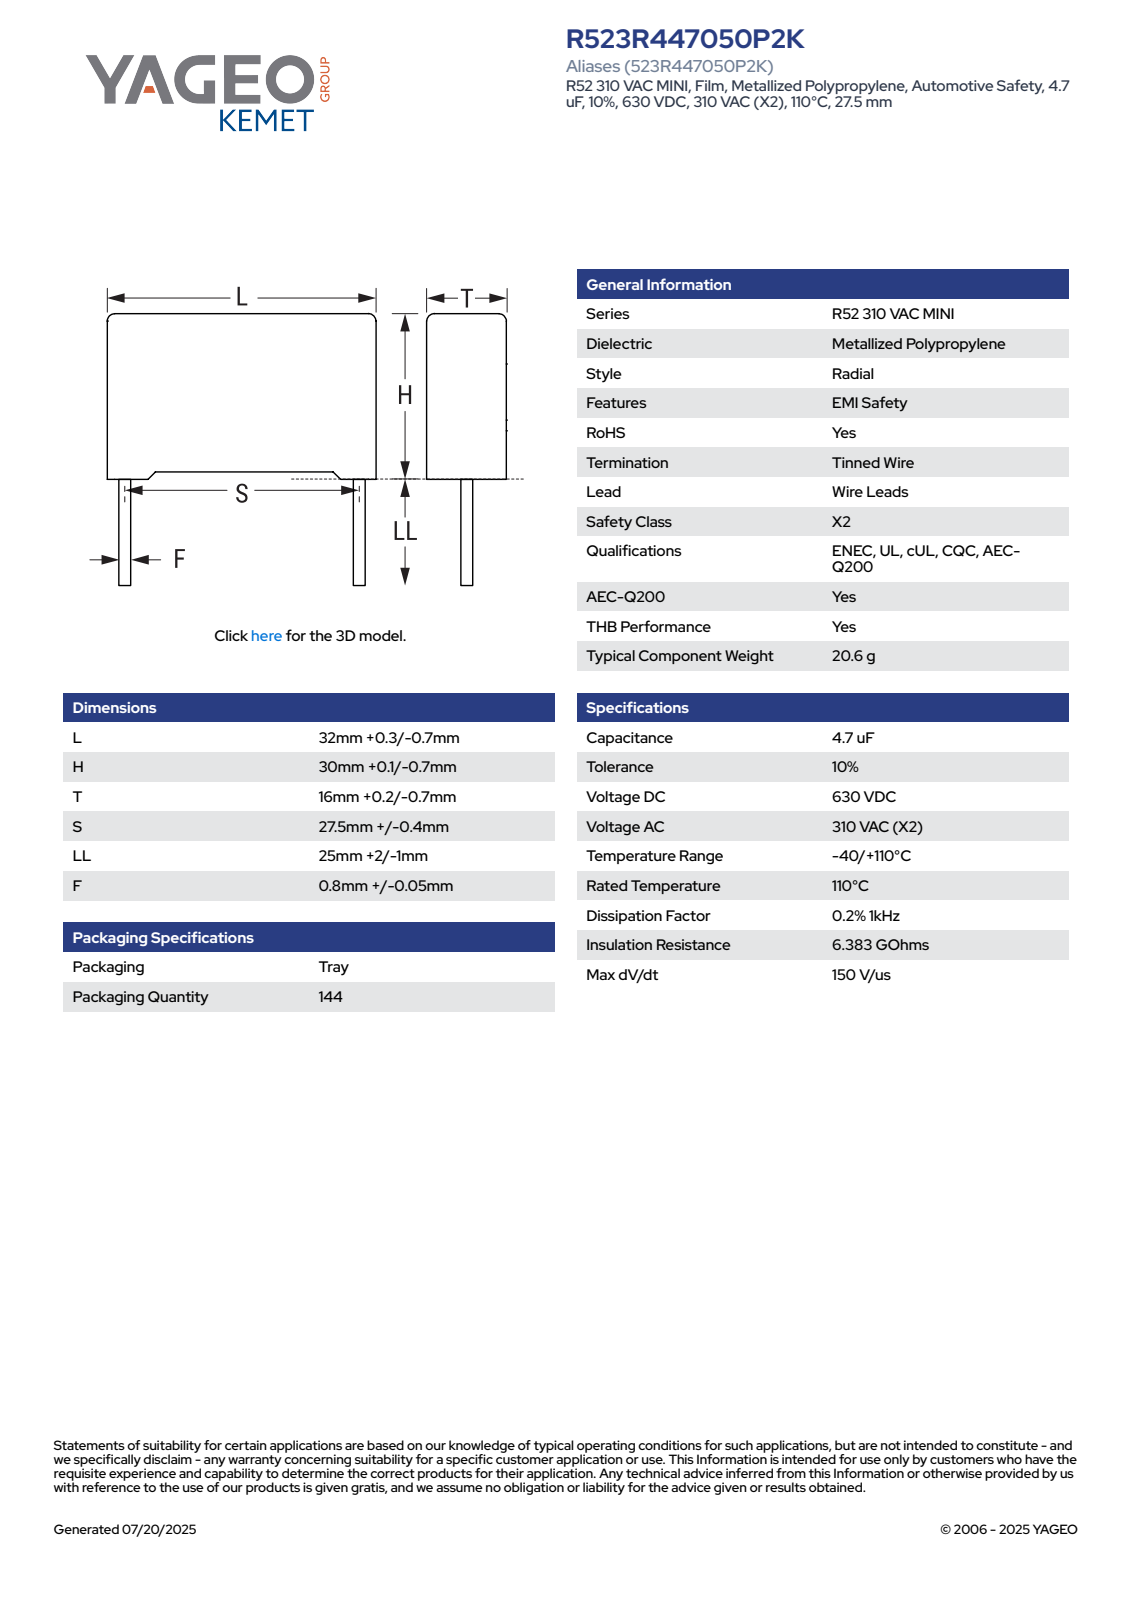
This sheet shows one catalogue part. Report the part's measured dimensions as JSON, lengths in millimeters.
{"part_name": "CFR_RB2_32X30X16_L32.3H30.1T16.2S27.5LL27F0.85", "step_written_by": "SolidWorks 2021 (AUTOMOTIVE_DESIGN)", "units": "millimeters", "bodies": {"solids": 4, "faces": 85, "planar": 77, "cylindrical": 8, "other": 0}, "overall_size": [57.1, 32.3, 16.2], "volume_mm3": 15314, "surface_area_mm2": 4159, "round_bosses_or_shafts": [[0.85, 2]], "partial_cylinders_radius": [[0.5, 4]], "face_to_face_distances": [16.2, 32.3, 29.06, 29.35, 0.75, 1.04, 30.1, 1.08, 31.22, 16.21]}
